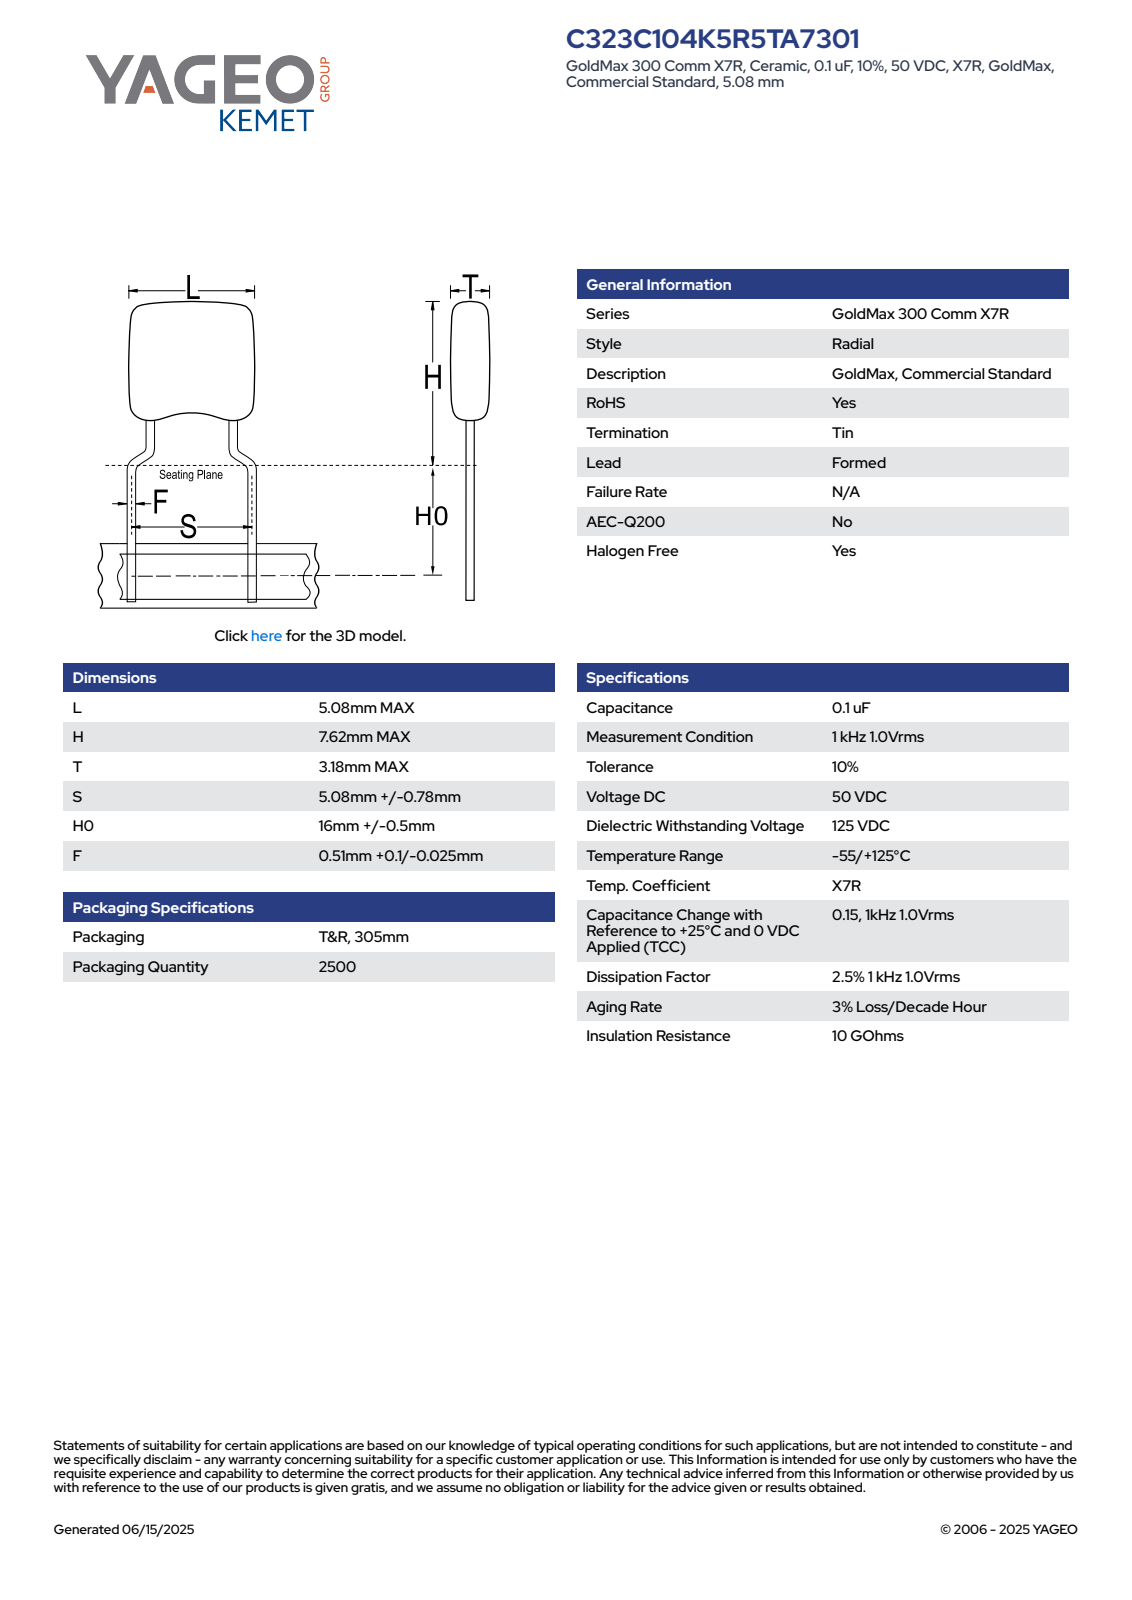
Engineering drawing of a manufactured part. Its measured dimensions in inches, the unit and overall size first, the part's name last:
Units: inches
Overall size (bounding box): 0.95 × 0.224 × 0.126
Round bosses / shafts (diameter × count): ⌀0.024 ×6
Partial cylindrical surfaces — rounded edges, fillets, slot ends (radius × count): R0.03 ×8, R0.039 ×2
Main face-to-face distances: 0.125, 0.2, 0.189, 0.76, 0.95, 0.126, 0.017, 0.864, 0.104, 0.085
Volume: 0.005 in³ · Surface area: 0.265 in²
Bodies: 4 solids, 109 faces (68 planar, 22 cylindrical, 19 other)
Part name (STEP PRODUCT): CCR_KRCHS_C323_L5.08H7.62T3.18S5.08H016.5F0.61
STEP written by: SolidWorks 2014 (AUTOMOTIVE_DESIGN)
